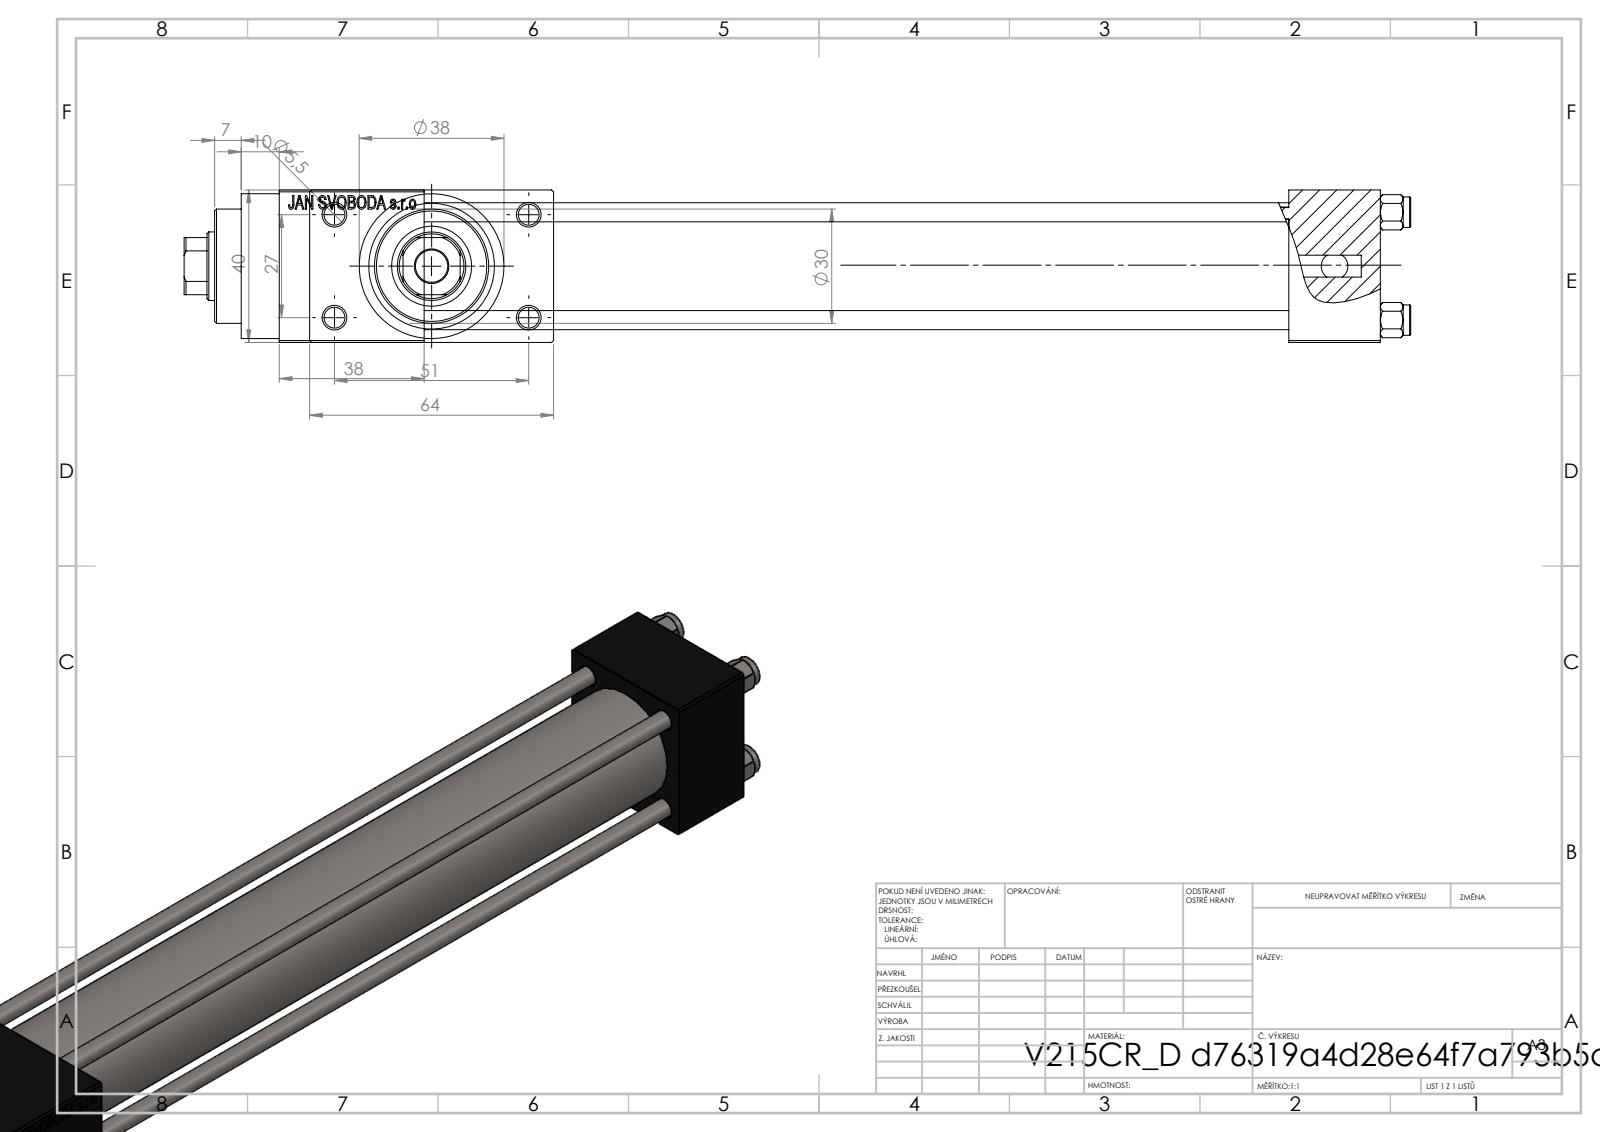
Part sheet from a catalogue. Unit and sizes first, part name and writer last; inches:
Units: inches
Overall size (bounding box): 12.677 × 2.52 × 1.575
Round holes (diameter × count): ⌀0.197 ×4, ⌀0.217 ×4, ⌀0.787 ×3, ⌀0.276 ×2, ⌀0.518 ×2, ⌀0.335 ×1, ⌀0.709 ×1, ⌀0.827 ×1, ⌀0.984 ×1, ⌀1.181 ×1
Round bosses / shafts (diameter × count): ⌀0.315 ×4, ⌀1.496 ×1, ⌀1.22 ×1
Partial cylindrical surfaces — rounded edges, fillets, slot ends (radius × count): R0.335 ×1
Main face-to-face distances: 1.575, 0.472, 8.937, 0.945, 9.882, 2.047, 1.496, 11.378, 10.433, 2.52
Hole centre spacings: 0.448, 0.788, 1.114, 1.136, 1.177, 1.561, 1.903, 1.063
Volume: 17.49 in³ · Surface area: 182.6 in²
Bodies: 11 solids, 1101 faces (495 planar, 86 cylindrical, 520 other)
Part name (STEP PRODUCT): V215_VC_A; V215CR_D_TYCINKA; V215CR_D_Body; NUT_M5_D (+1 more)
STEP written by: SolidWorks 2019 (CONFIG_CONTROL_DESIGN)
